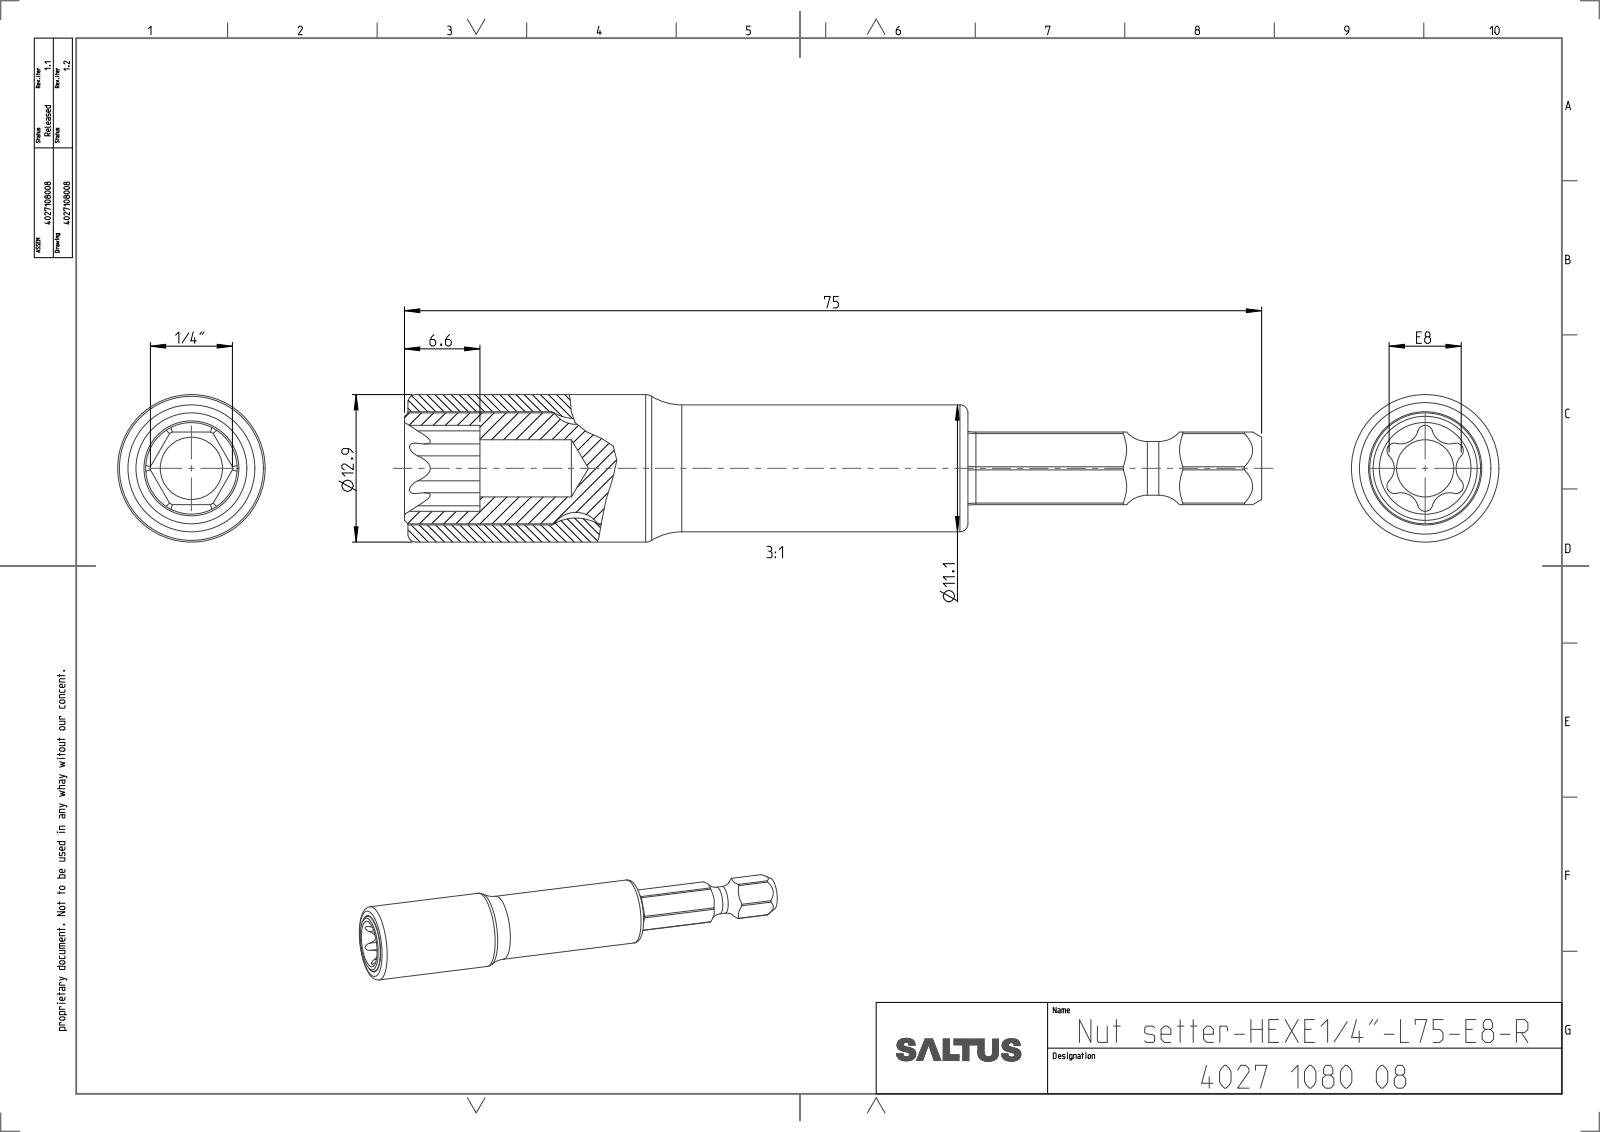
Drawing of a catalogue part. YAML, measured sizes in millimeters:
part_name: "4027911286; 4027299452; 4027108008_ASM"
step_written_by: "CREO PARAMETRIC BY PTC INC, 2022414 (CONFIG_CONTROL_DESIGN)"
units: millimeters
bodies: {solids: 2, faces: 103, planar: 17, cylindrical: 50, other: 36}
overall_size: [75, 12.9, 12.9]
volume: 5704
surface_area: 5559
round_holes:
  - {diameter: 5, count: 1}
  - {diameter: 8.3, count: 1}
  - {diameter: 9.9, count: 1}
round_bosses_or_shafts:
  - {diameter: 12.9, count: 1}
  - {diameter: 11.1, count: 1}
  - {diameter: 9.7, count: 1}
  - {diameter: 8, count: 1}
  - {diameter: 4.7, count: 1}
partial_cylinders:
  - {radius: 0.66, count: 6}
  - {radius: 1.55, count: 6}
  - {radius: 5, count: 6}
  - {radius: 3.59, count: 1}
face_to_face_distances: [6.34, 6.36, 74.7, 25.7, 49, 75, 49.3, 68.4, 42.7, 6.3]
